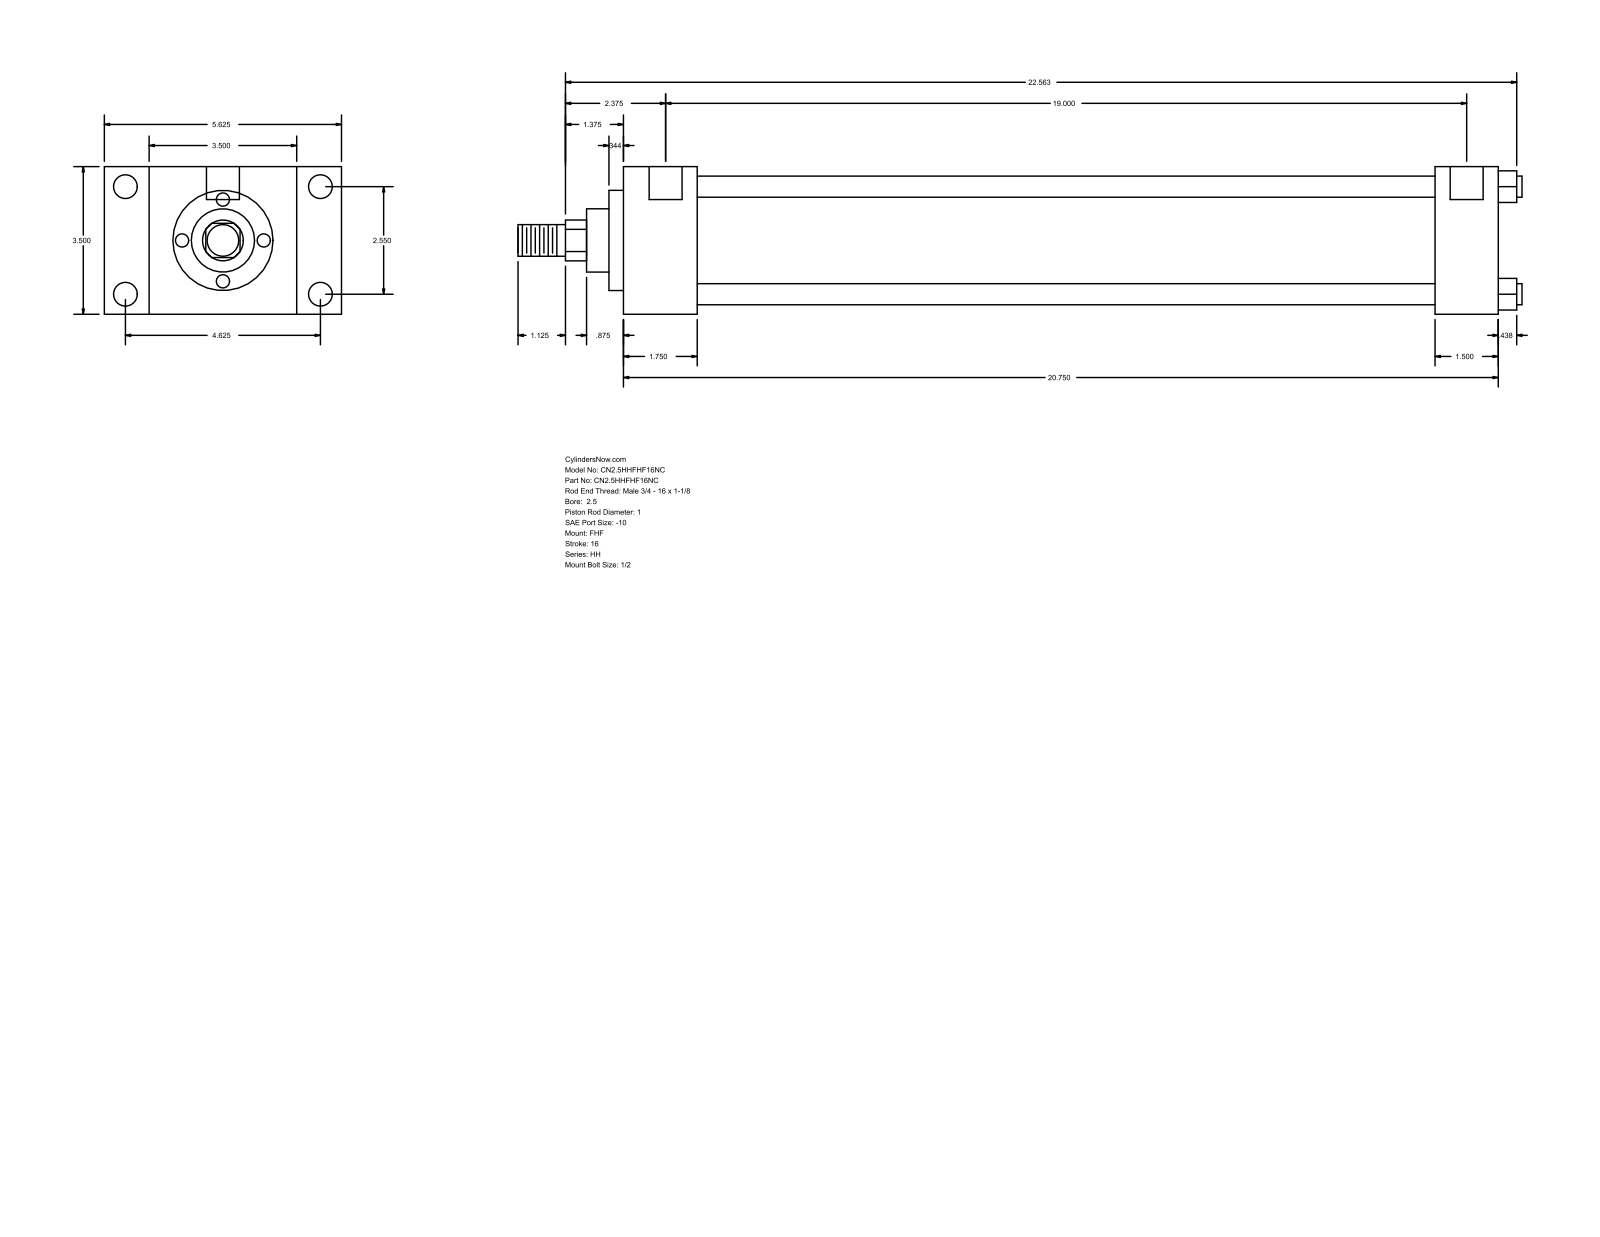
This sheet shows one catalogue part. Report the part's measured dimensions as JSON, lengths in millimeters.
{"part_name": "HH_FHF__0250_1", "step_written_by": "GSSL Pune (CONFIG_CONTROL_DESIGN)", "units": "millimeters", "bodies": {"solids": 0, "faces": 90, "planar": 61, "cylindrical": 29, "other": 0}, "overall_size": [604.84, 142.88, 88.9], "round_holes": [[5.56, 4], [14.3, 4], [19.84, 2]], "round_bosses_or_shafts": [[12.7, 4], [73.03, 1], [60.33, 1], [38.1, 1], [25.4, 1], [19.05, 1]], "partial_cylinders_radius": [[12.29, 1]], "face_to_face_distances": [88.9, 44.46, 26.99, 115.89, 527.06, 482.6, 142.88, 38.1, 488.96, 444.5], "hole_center_spacings": [1.59, 64.76, 117.48, 134.15, 484.18, 485.77, 482.59]}
